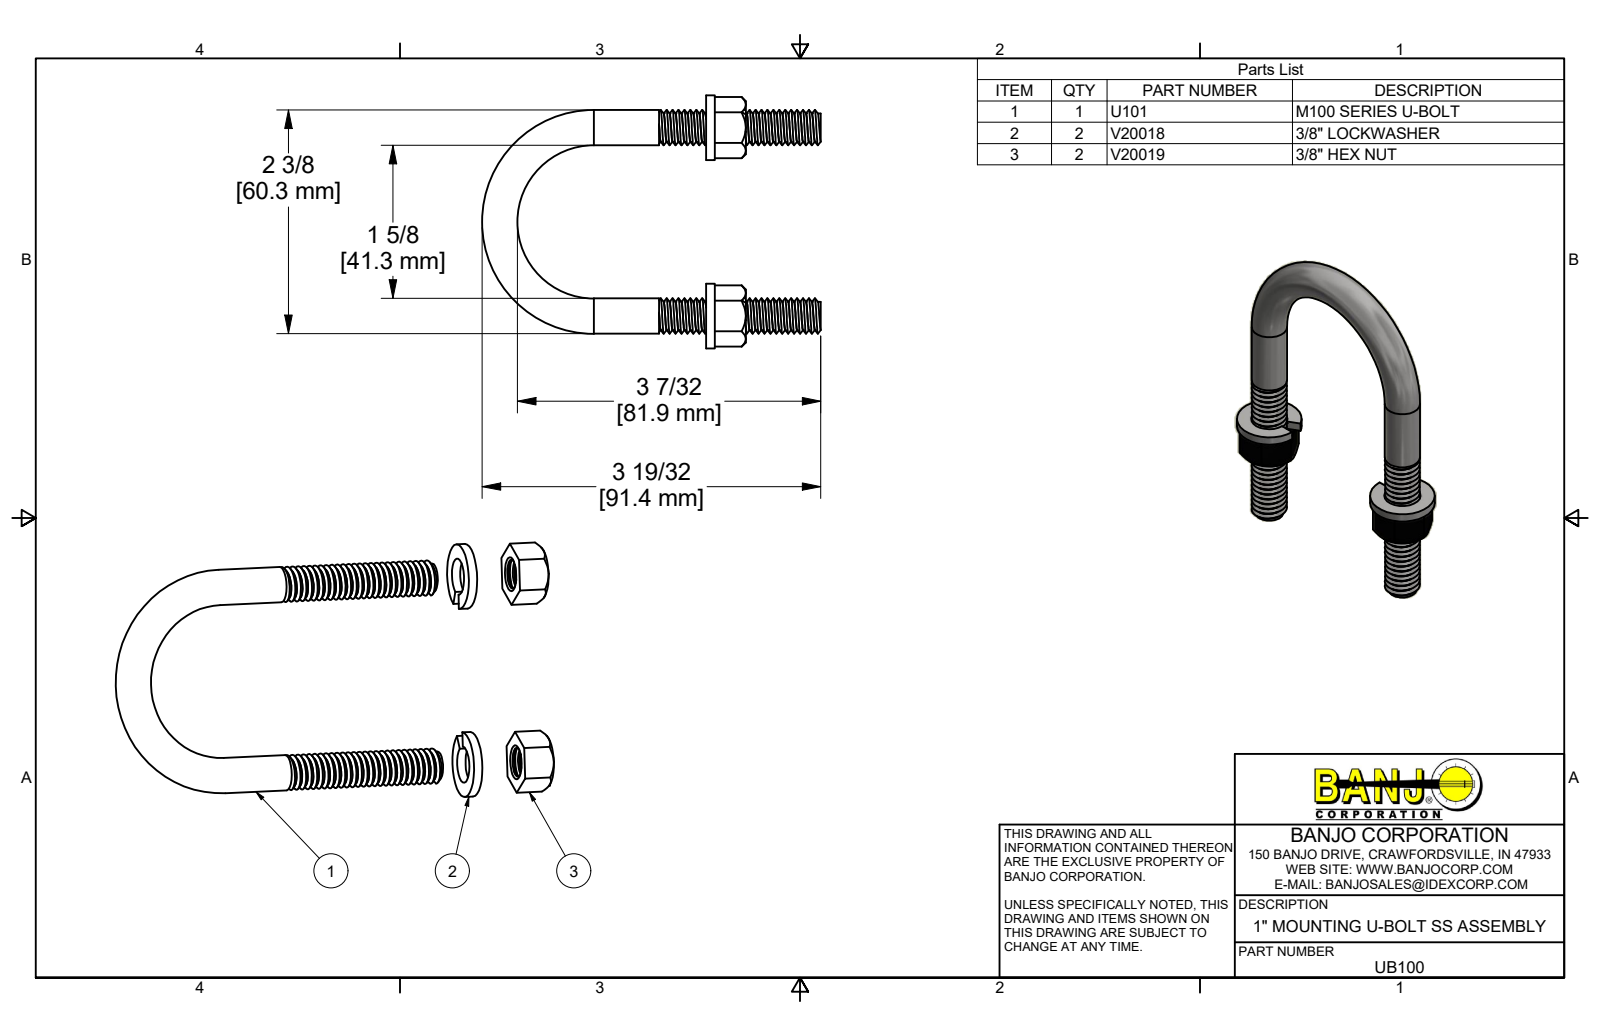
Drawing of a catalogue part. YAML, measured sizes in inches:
part_name: "UB100; U101; V20018; V20019"
step_written_by: "Autodesk Inventor 2019 (AUTOMOTIVE_DESIGN)"
units: inches
bodies: {solids: 7, faces: 201, planar: 32, cylindrical: 102, other: 67}
overall_size: [3.598, 2.688, 0.688]
volume: 0.972
surface_area: 16.12
round_holes:
  - {diameter: 0.307, count: 2}
  - {diameter: 0.375, count: 2}
  - {diameter: 0.385, count: 2}
round_bosses_or_shafts:
  - {diameter: 0.687, count: 2}
  - {diameter: 0.3, count: 2}
face_to_face_distances: [0.094, 1.732, 0.563, 0.594, 0.5, 0.328, 0.422, 0.922, 0.562, 2.294]
hole_center_spacings: [2]
